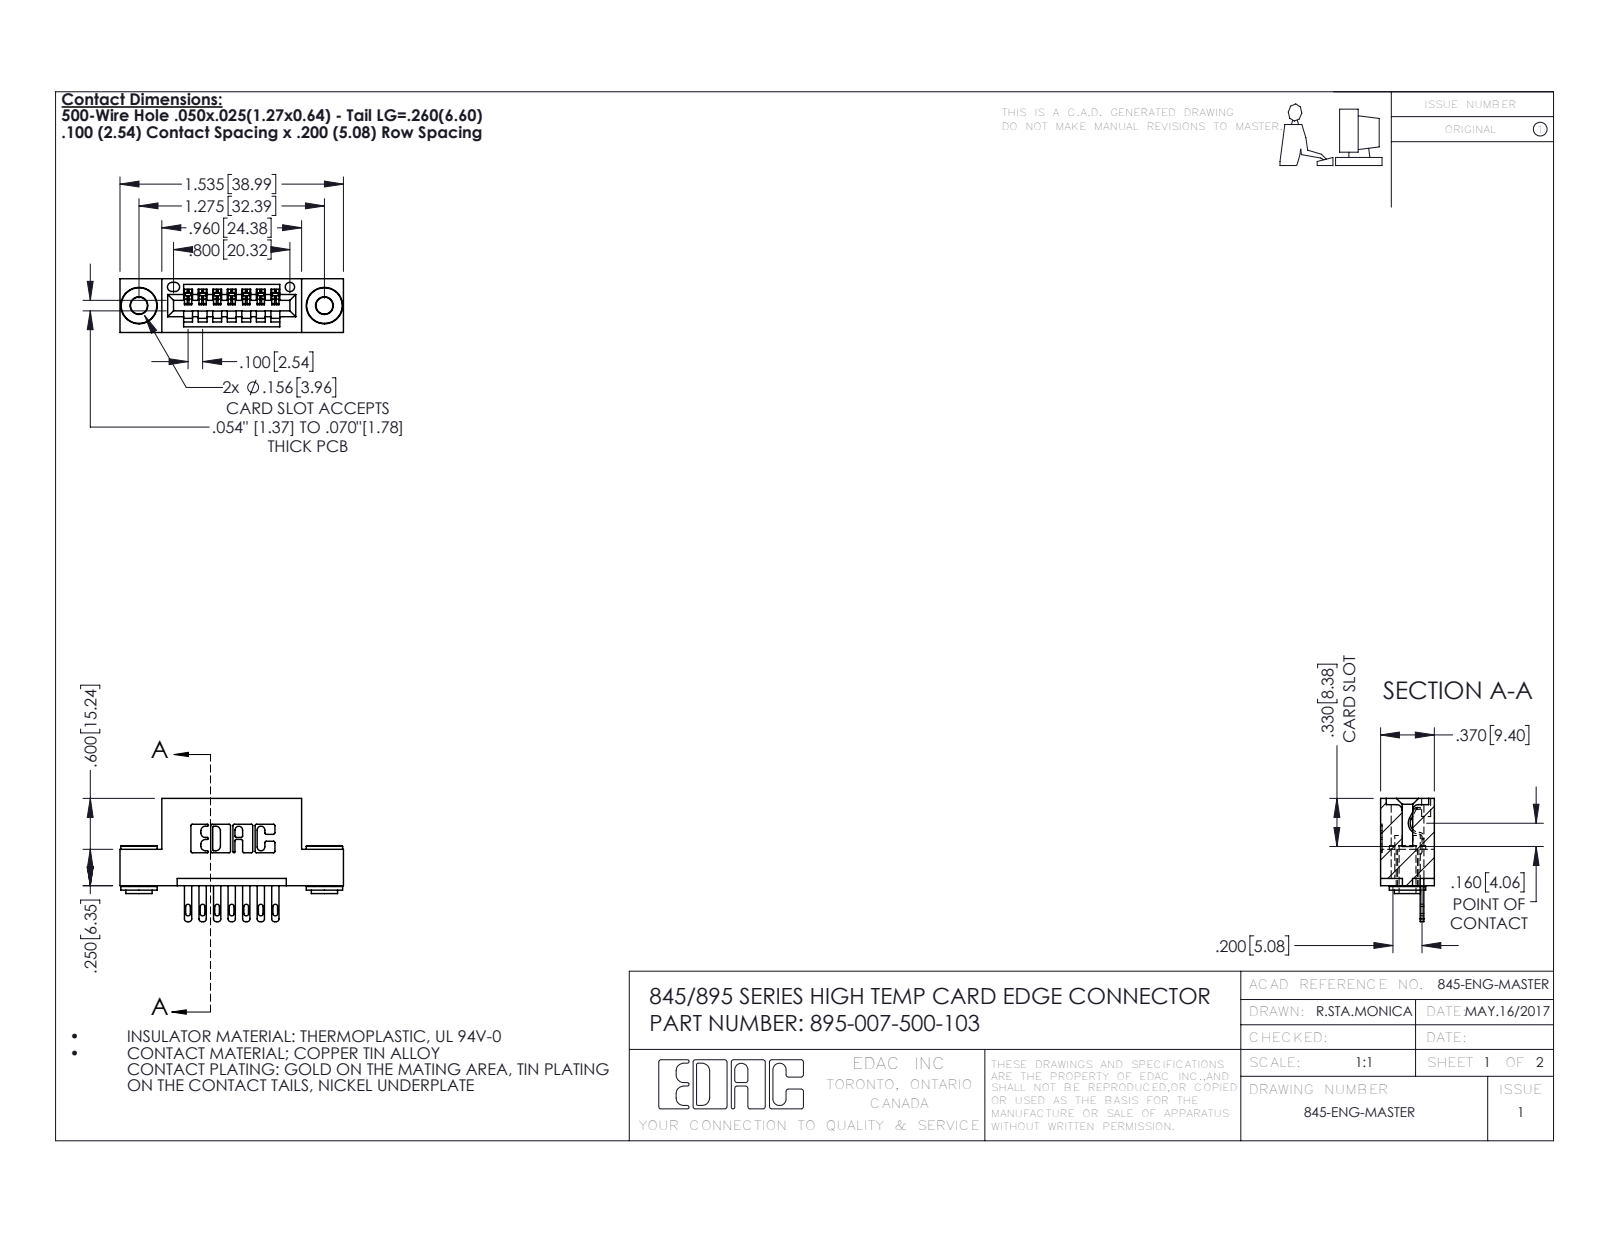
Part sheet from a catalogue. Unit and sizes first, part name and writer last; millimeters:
Units: millimetres
Overall size (bounding box): 39 × 21.5 × 9.4
Round holes (diameter × count): ⌀2.9 ×2, ⌀4 ×2, ⌀1.6 ×1
Round bosses / shafts (diameter × count): ⌀6.4 ×2, ⌀4.6 ×2, ⌀3.5 ×2
Partial cylindrical surfaces — rounded edges, fillets, slot ends (radius × count): R0.3 ×22, R0.2 ×14, R0.4 ×14, R0.5 ×14, R0.2 ×6, R0.8 ×6, R0.7 ×3, R0.8 ×2
Main face-to-face distances: 5.1, 9.4, 1.8, 7.6, 2.5, 0.6, 7.6, 2.5, 6.9, 6.4
Hole centre spacings: 6.9, 26.5, 32.4
Volume: 3 440 mm³ · Surface area: 4 326 mm²
Bodies: 10 solids, 542 faces (328 planar, 206 cylindrical, 8 other)
Part name (STEP PRODUCT): 895-007-500-103; 345-250-002_345-250-002-102; 845 Part_Flush Mounting Lugs - 0.156 Dia-TH; 345-292-001_345-293-100
STEP written by: SolidWorks 2020 (CONFIG_CONTROL_DESIGN)
